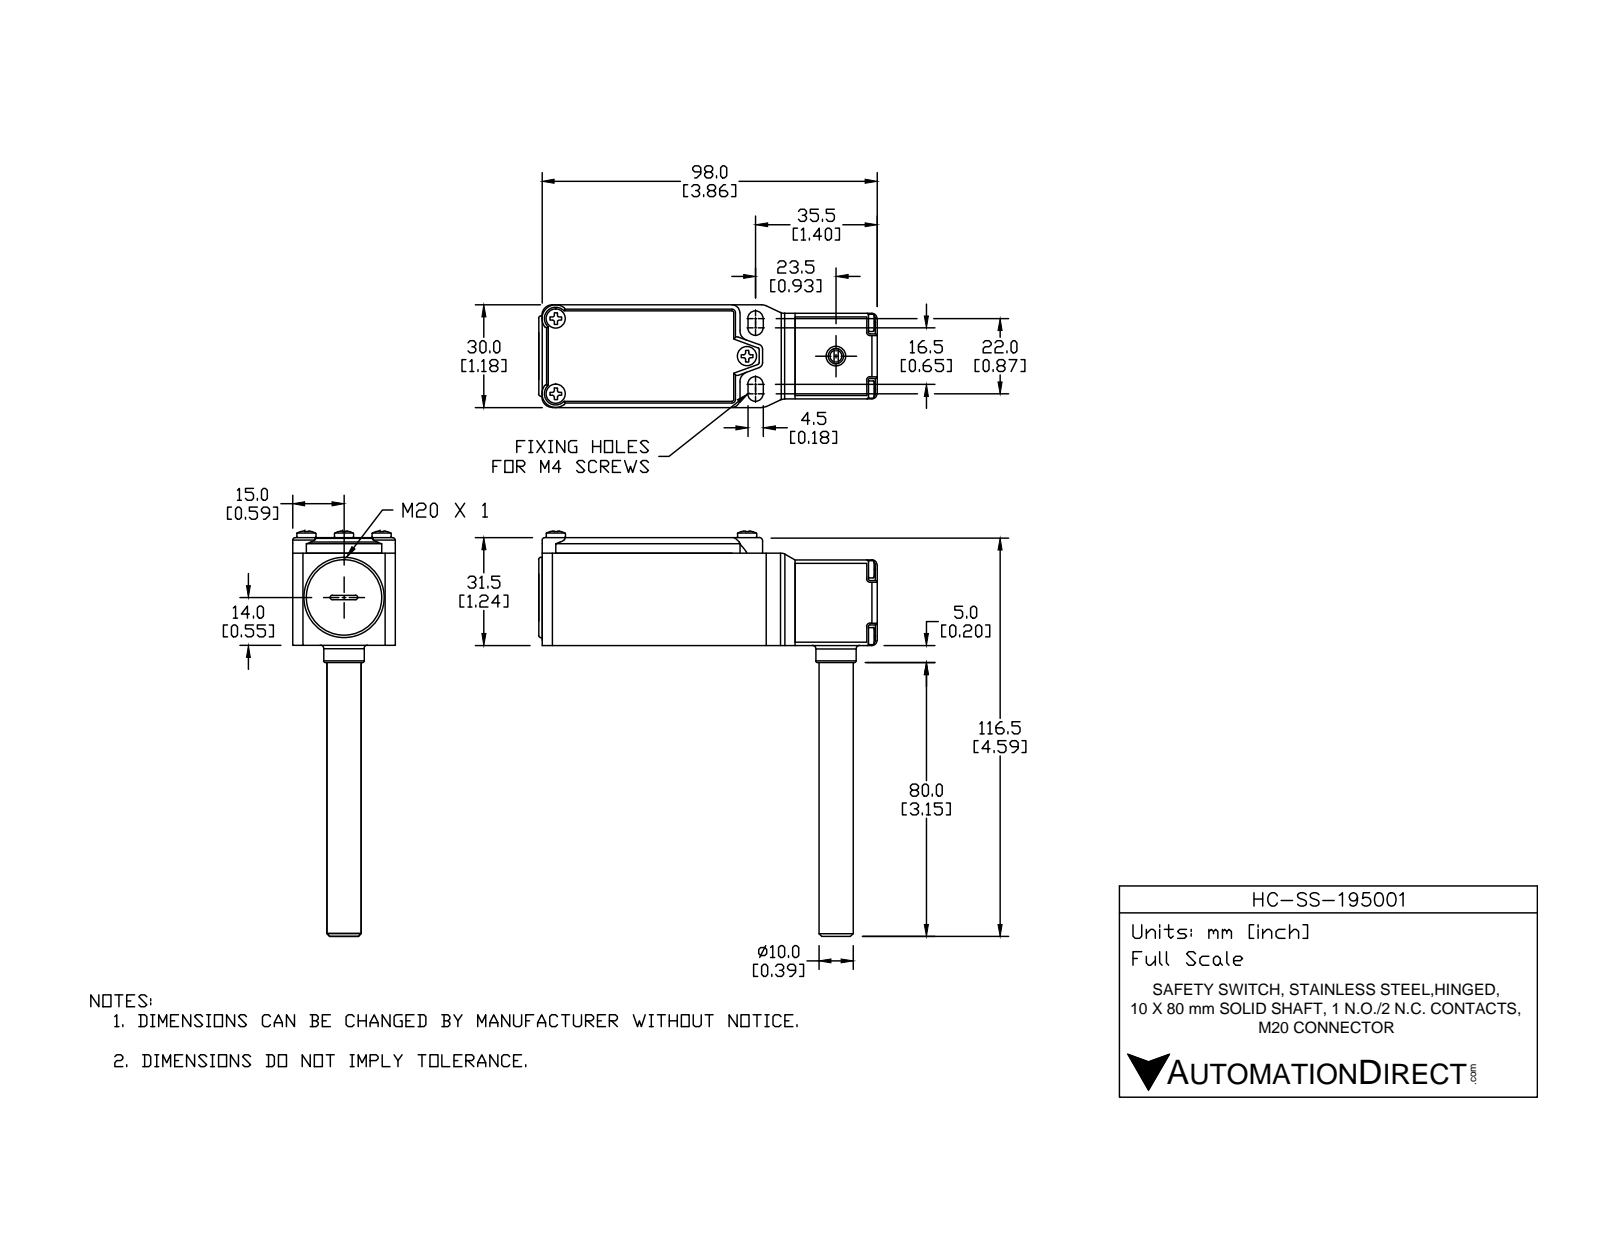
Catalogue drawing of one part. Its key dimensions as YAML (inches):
part_name: "HC-SS-195001"
step_written_by: "SolidWorks 2014 (AUTOMOTIVE_DESIGN)"
units: inches
bodies: {solids: 13, faces: 1168, planar: 347, cylindrical: 466, other: 355}
overall_size: [4.663, 3.898, 1.181]
volume: 2.792
surface_area: 54.45
round_holes:
  - {diameter: 0.098, count: 8}
  - {diameter: 0.126, count: 7}
  - {diameter: 0.157, count: 3}
  - {diameter: 0.059, count: 2}
  - {diameter: 0.071, count: 2}
  - {diameter: 0.087, count: 2}
  - {diameter: 0.142, count: 2}
  - {diameter: 0.081, count: 1}
  - {diameter: 0.114, count: 1}
  - {diameter: 0.173, count: 1}
  - {diameter: 0.185, count: 1}
  - {diameter: 0.217, count: 1}
round_bosses_or_shafts:
  - {diameter: 0.118, count: 7}
  - {diameter: 0.197, count: 5}
  - {diameter: 0.138, count: 4}
  - {diameter: 0.22, count: 3}
  - {diameter: 0.925, count: 1}
  - {diameter: 0.697, count: 1}
  - {diameter: 0.394, count: 1}
  - {diameter: 0.386, count: 1}
partial_cylinders:
  - {radius: 0.02, count: 175}
  - {radius: 0.039, count: 20}
  - {radius: 0.012, count: 18}
  - {radius: 0.006, count: 14}
  - {radius: 0.028, count: 8}
  - {radius: 0.118, count: 8}
  - {radius: 0.059, count: 6}
  - {radius: 0.089, count: 4}
face_to_face_distances: [0.098, 1.142, 0.079, 0.114, 1.067, 1.181, 0.177, 1.24, 0.016, 1.083]
hole_center_spacings: [0.543, 0.768, 0.187, 0.245, 0.414, 0.423, 0.426, 0.476]
